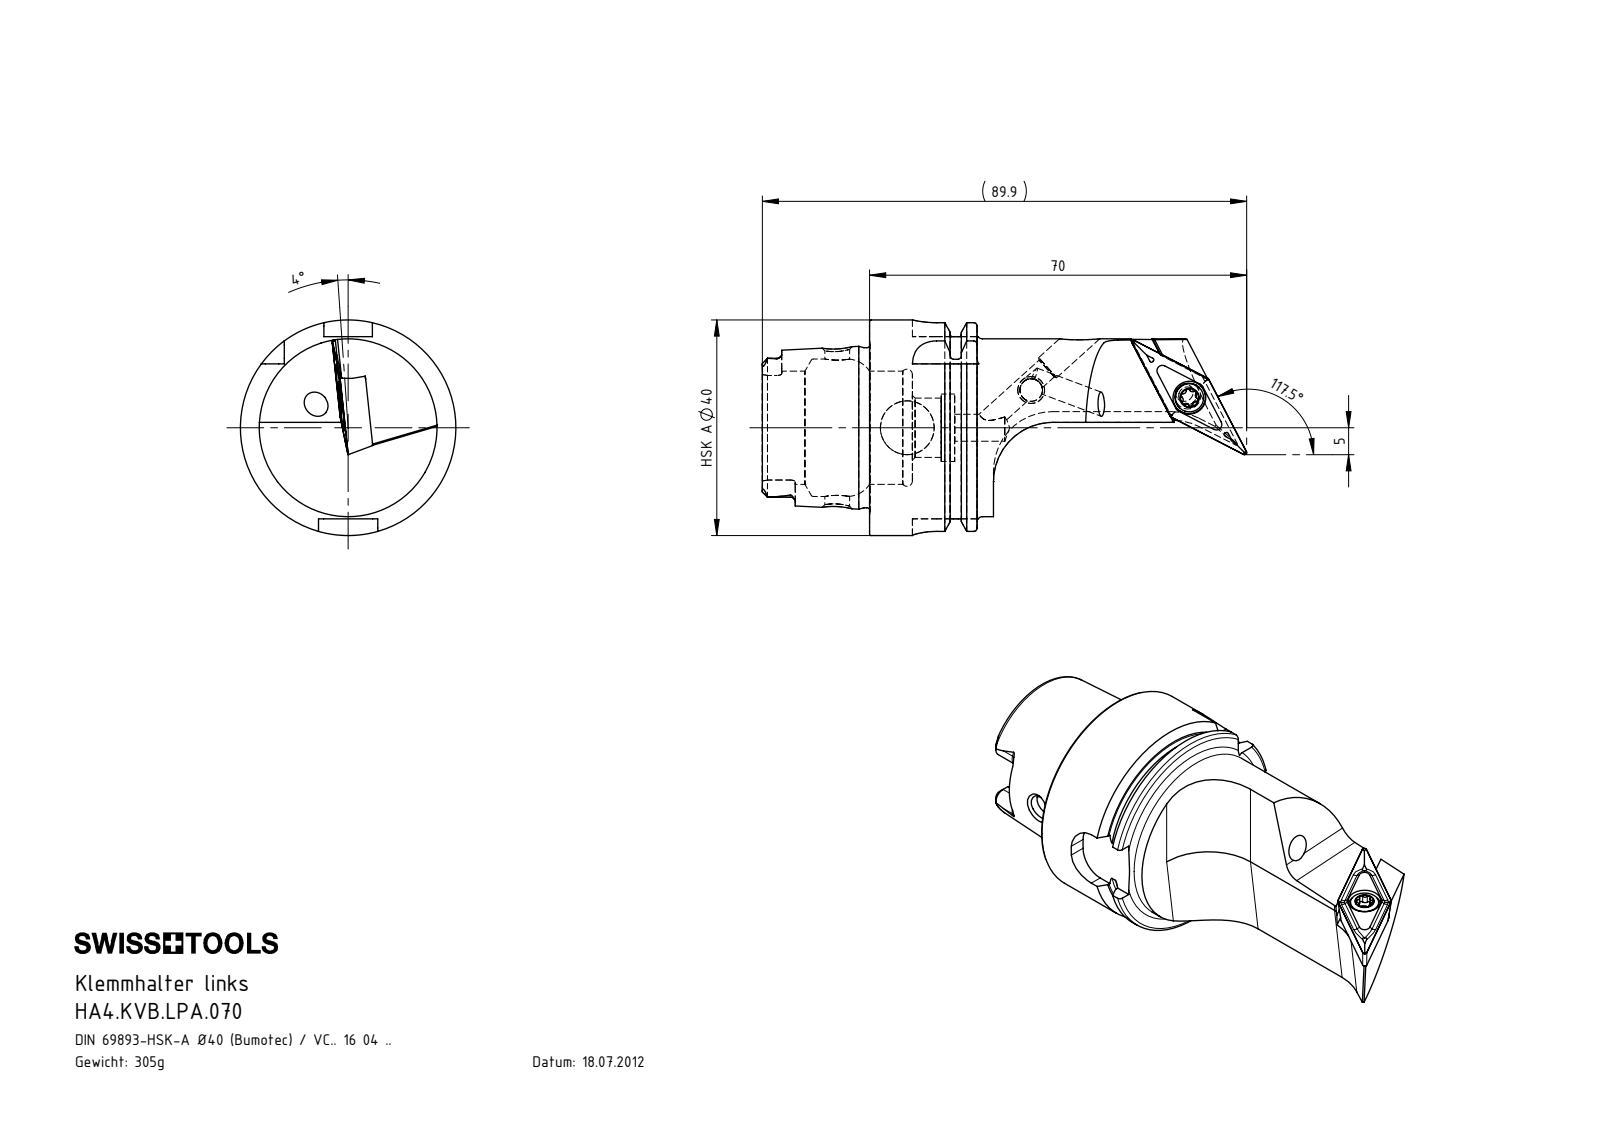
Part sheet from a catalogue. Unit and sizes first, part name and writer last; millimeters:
Units: millimetres
Overall size (bounding box): 89.9 × 40 × 40
Round holes (diameter × count): ⌀4.2 ×3, ⌀4 ×2, ⌀5 ×2, ⌀3.3 ×1, ⌀4.4 ×1, ⌀4.6 ×1, ⌀6.1 ×1, ⌀10 ×1, ⌀11 ×1, ⌀12.5 ×1, ⌀21 ×1, ⌀25.5 ×1
Round bosses / shafts (diameter × count): ⌀5 ×2, ⌀40 ×1, ⌀34.75 ×1, ⌀33 ×1, ⌀29.71 ×1, ⌀5.25 ×1, ⌀4 ×1
Partial cylindrical surfaces — rounded edges, fillets, slot ends (radius × count): R0.34 ×6, R0.59 ×6, R0.9 ×6, R1.88 ×4, R4.5 ×4, R11 ×2, R3 ×1
Main face-to-face distances: 7.95, 19.95, 12, 19.9, 27.85, 39.85, 42.9, 23, 15.05, 3.05
Hole centre spacings: 24.04
Volume: 38 349 mm³ · Surface area: 14 658 mm²
Bodies: 7 solids, 262 faces (85 planar, 63 cylindrical, 114 other)
Part name (STEP PRODUCT): WCB-ER2.001.009_A; VCMT160404; HA4-KVB.LPA.070_A_Fertigbearbeitung; HA4.KVB.LPA.070 (+1 more)
STEP written by: SolidWorks 2017 (AUTOMOTIVE_DESIGN)
